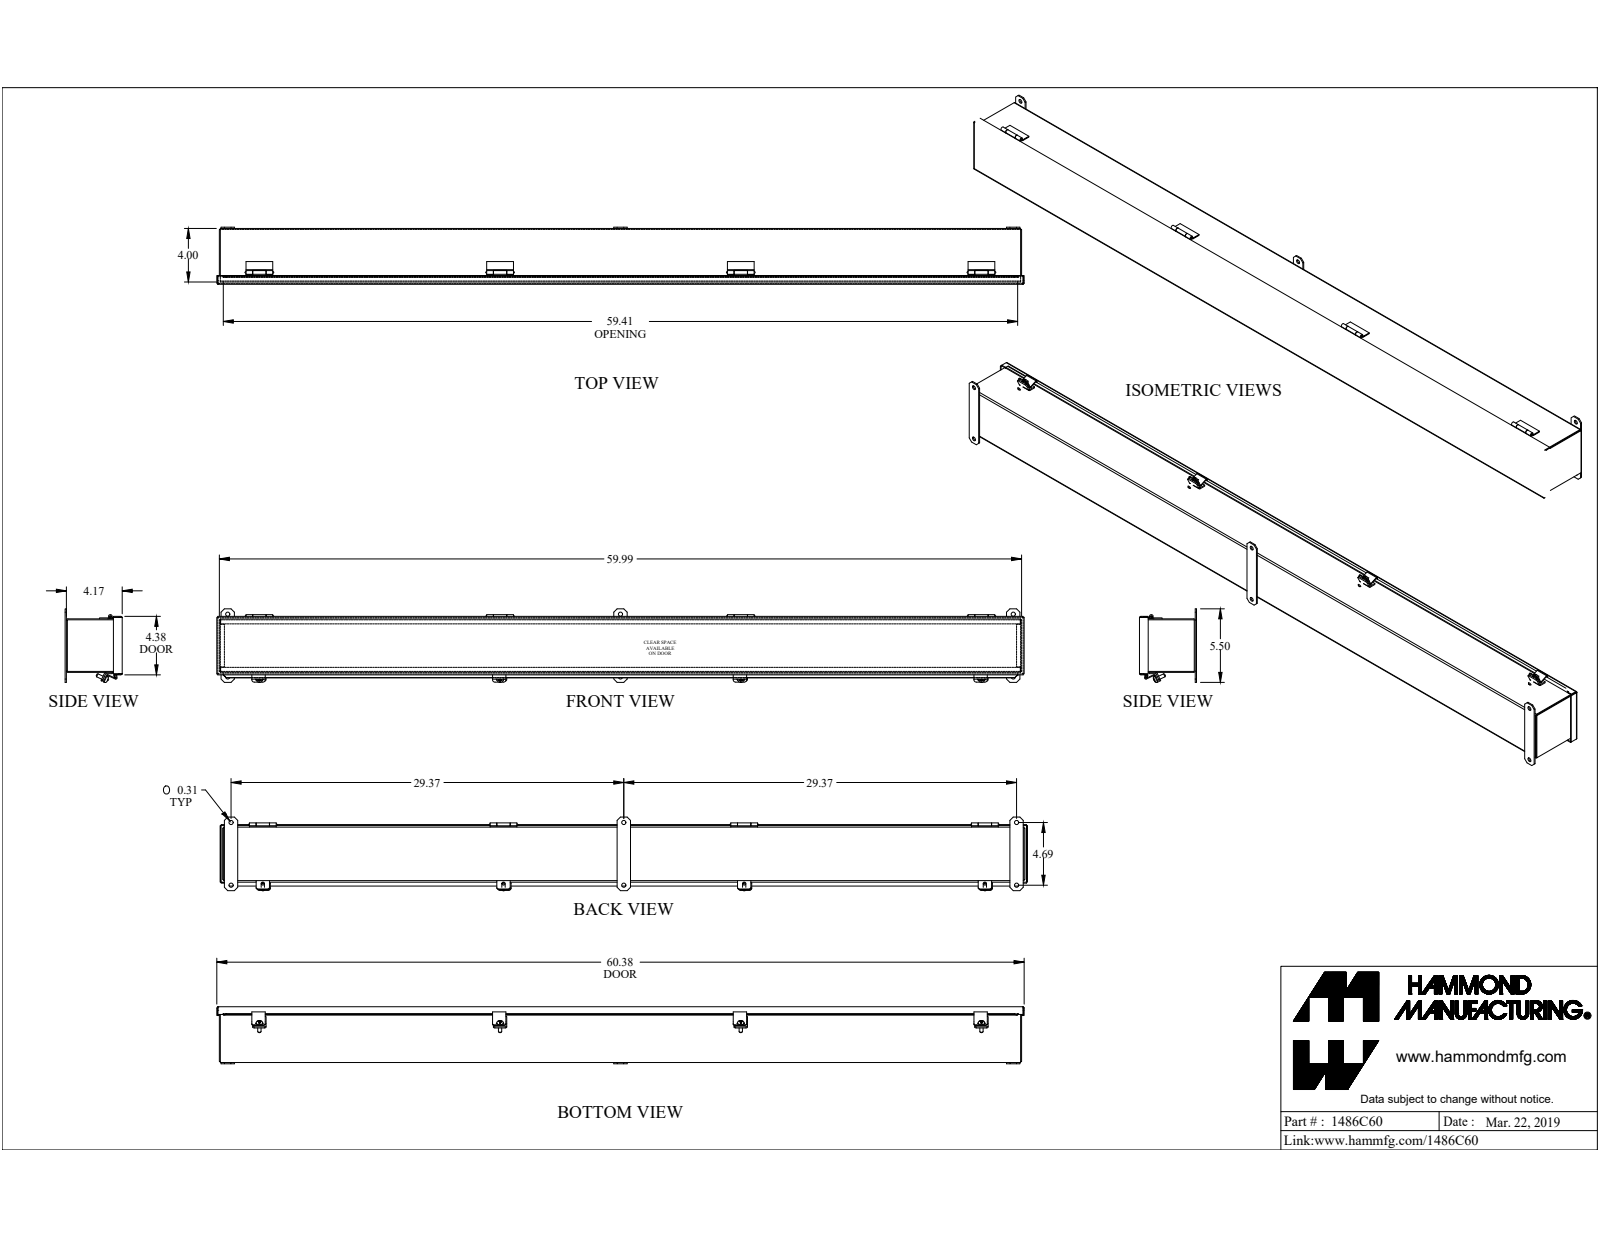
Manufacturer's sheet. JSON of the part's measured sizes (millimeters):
{"part_name": "1486C60", "step_written_by": "SolidWorks 2019 (CONFIG_CONTROL_DESIGN)", "units": "millimeters", "bodies": {"solids": 35, "faces": 628, "planar": 442, "cylindrical": 132, "other": 54}, "overall_size": [1533.5, 139.9, 108.4], "volume_mm3": 1668000, "surface_area_mm2": 1673000, "round_holes": [[8, 6], [5.4, 4], [3.2, 1]], "round_bosses_or_shafts": [[12.2, 4], [6.2, 4], [7, 1]], "partial_cylinders_radius": [[4.8, 16], [0.9, 11], [2.7, 11], [0.3, 8], [3.6, 8], [0.7, 2], [2.2, 2], [1.2, 1]], "face_to_face_distances": [1.8, 99.8, 104.1, 101.6, 97.9, 106, 102.3, 99.4, 97.6, 4.7], "hole_center_spacings": [746, 755.5, 119.1, 457.2, 914.4, 1492.1, 1496.8, 1371.6]}
